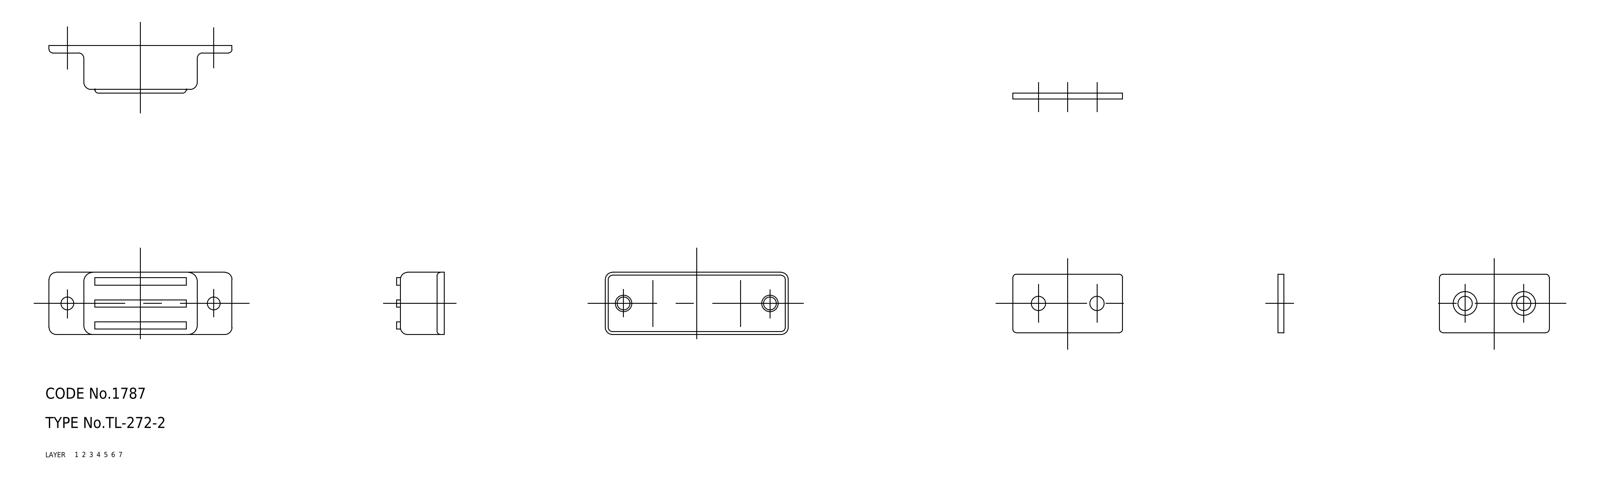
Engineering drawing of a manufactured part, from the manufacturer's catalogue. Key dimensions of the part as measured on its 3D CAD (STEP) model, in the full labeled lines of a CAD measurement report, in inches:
Part name (STEP PRODUCT): attachment; keeper; housing; base (+1 more)
STEP written by: CADfix (AUTOMOTIVE_DESIGN)
Units: inches
Bodies: 6 solids, 167 faces (0 planar, 0 cylindrical, 167 other)
Overall size (bounding box): 1.969 × 1.274 × 0.669
Volume: 0.247 in³ · Surface area: 12.75 in²
